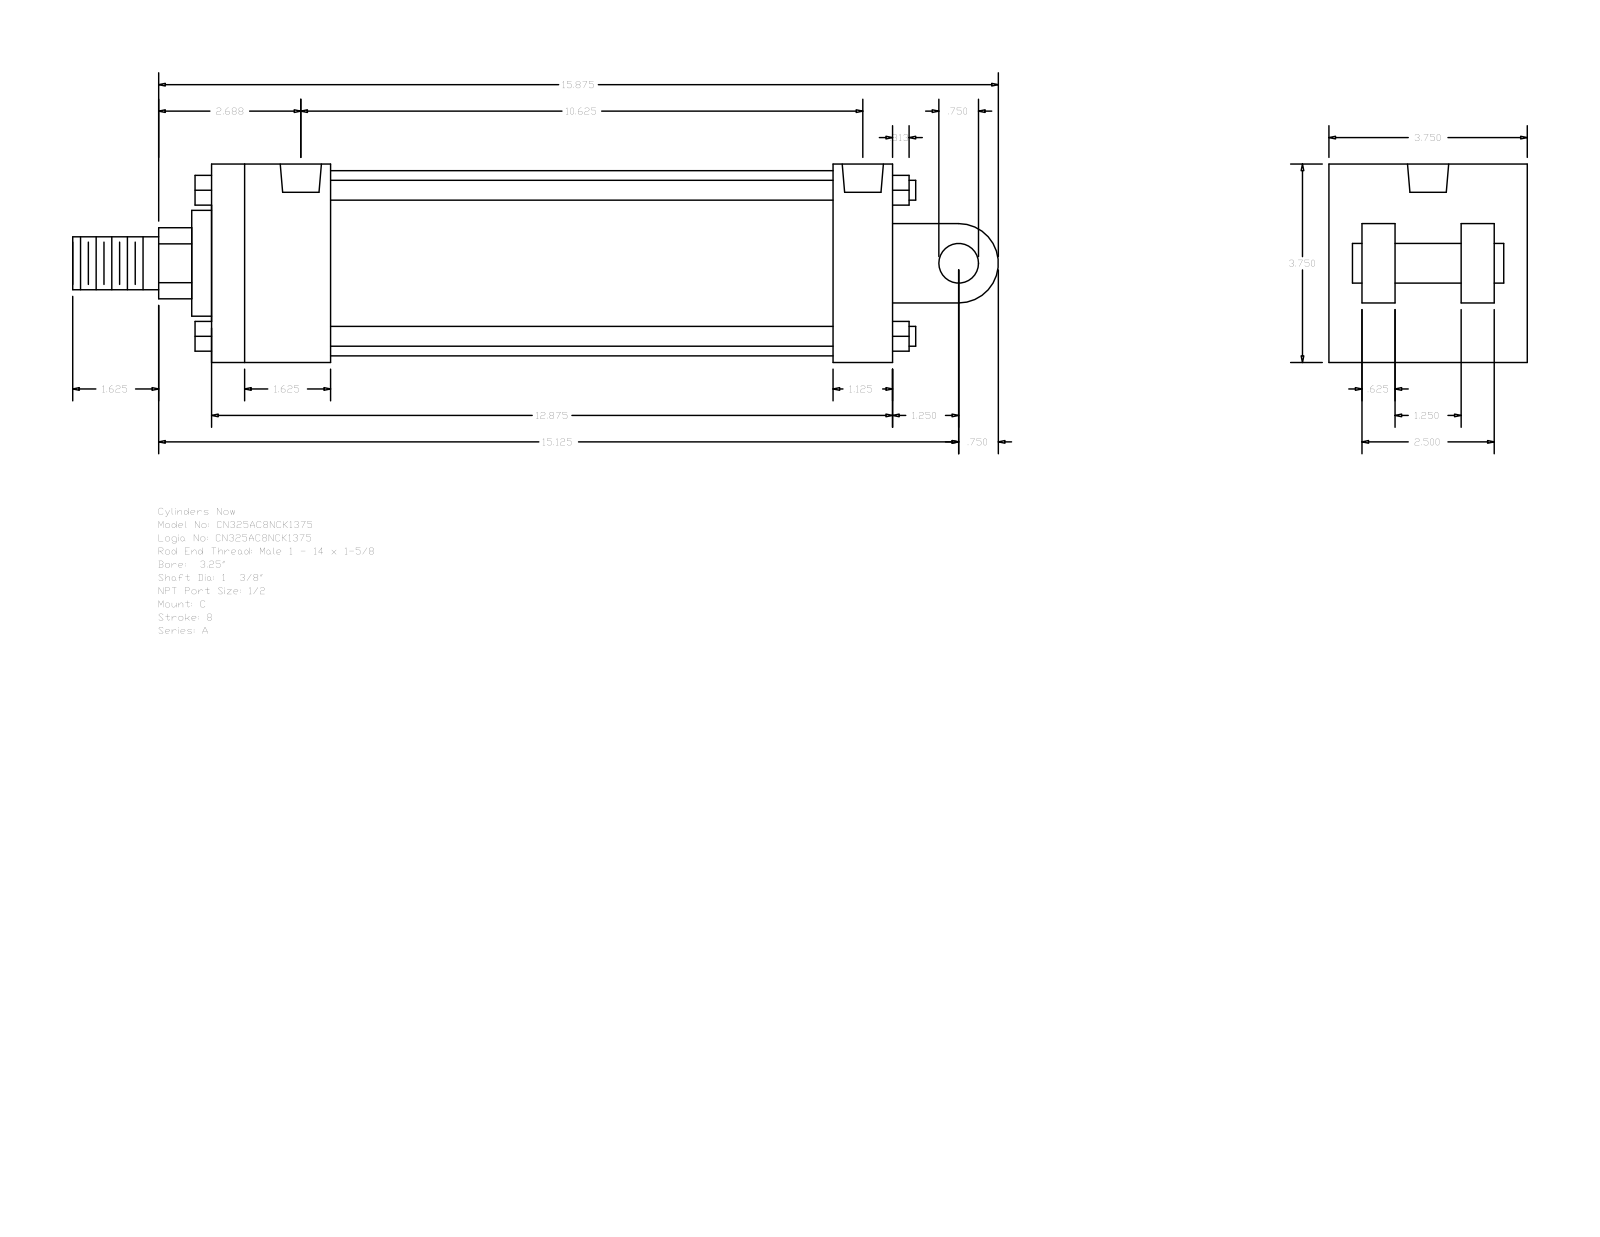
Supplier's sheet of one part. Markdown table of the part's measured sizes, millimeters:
| quantity | value |
| --- | --- |
| part name | A_C__0325_1.375 |
| STEP written by | GSSL Pune (CONFIG_CONTROL_DESIGN) |
| units | millimeters |
| bodies | 0 solids, 135 faces (102 planar, 33 cylindrical, 0 other) |
| overall size | 444.5 × 95.25 × 95.25 |
| round holes (diameter × count) | 8.73 × 4, 19.77 × 2 |
| round bosses / shafts (diameter × count) | 9.53 × 4, 88.9 × 1, 50.8 × 1, 34.92 × 1, 25.4 × 1, 19.05 × 1 |
| partial cylindrical surfaces (radius × count) | 17.06 × 1, 19.05 × 1 |
| main face-to-face distances | 95.24, 327.03, 15.87, 63.5, 66.67, 57.15, 28.58, 79.37, 31.74, 47.63 |
| hole center spacings | 3.18, 263.52, 266.7, 269.88 |
